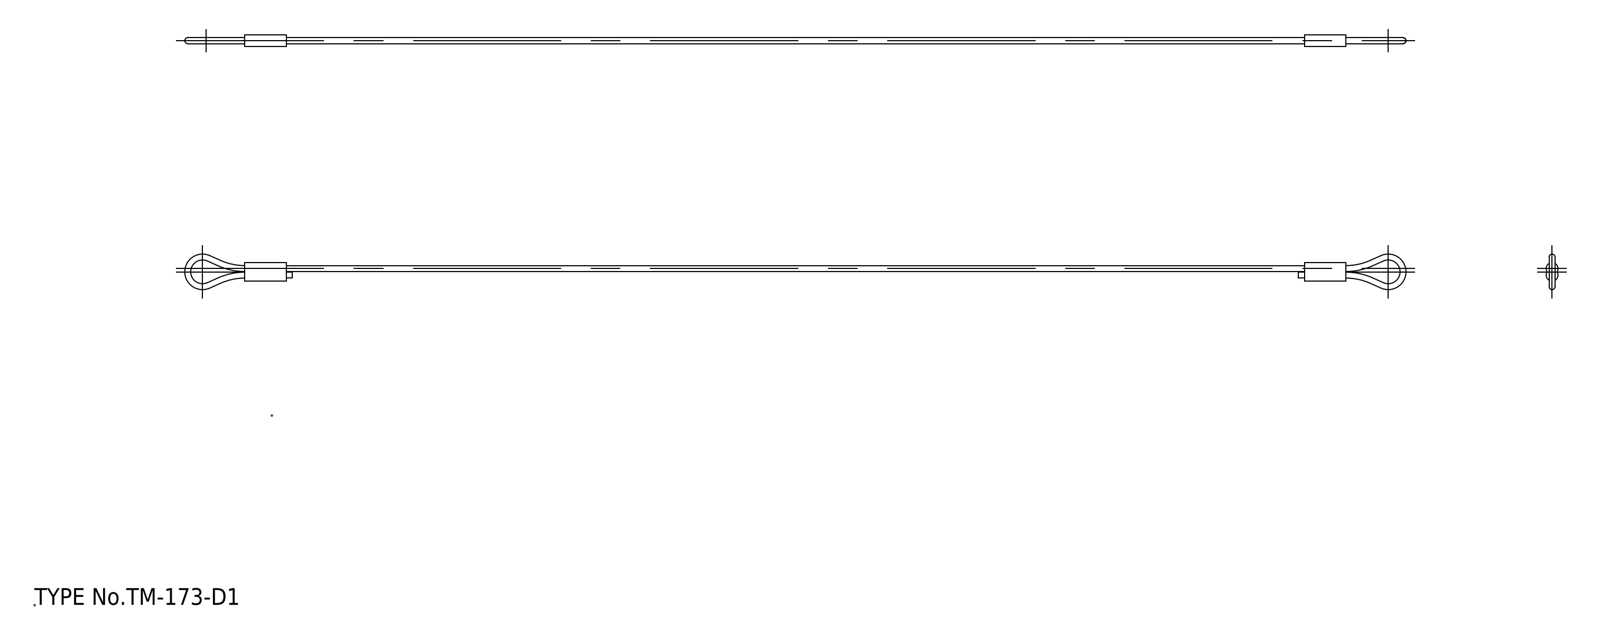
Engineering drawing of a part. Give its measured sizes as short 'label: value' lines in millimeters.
name: PC013-prt0; PC013-prt1; PC013-prt2; PC013-prt3 (+3 more)
written by: spGate 19.8.4 (****-****-****-****) (AUTOMOTIVE_DESIGN)
unit: mm
bodies: 3 solids, 48 faces (6 planar, 30 cylindrical, 12 other)
size: 206 × 6 × 2
volume: 244 mm³; area: 989 mm²
holes: 1× ⌀1
bosses: 5× ⌀1
rounds: 2× R0.25, 2× R0.5, 2× R1
face distances: 178.74, 7, 185.74, 171.74, 8, 177.74, 1, 170.74, 169.74
